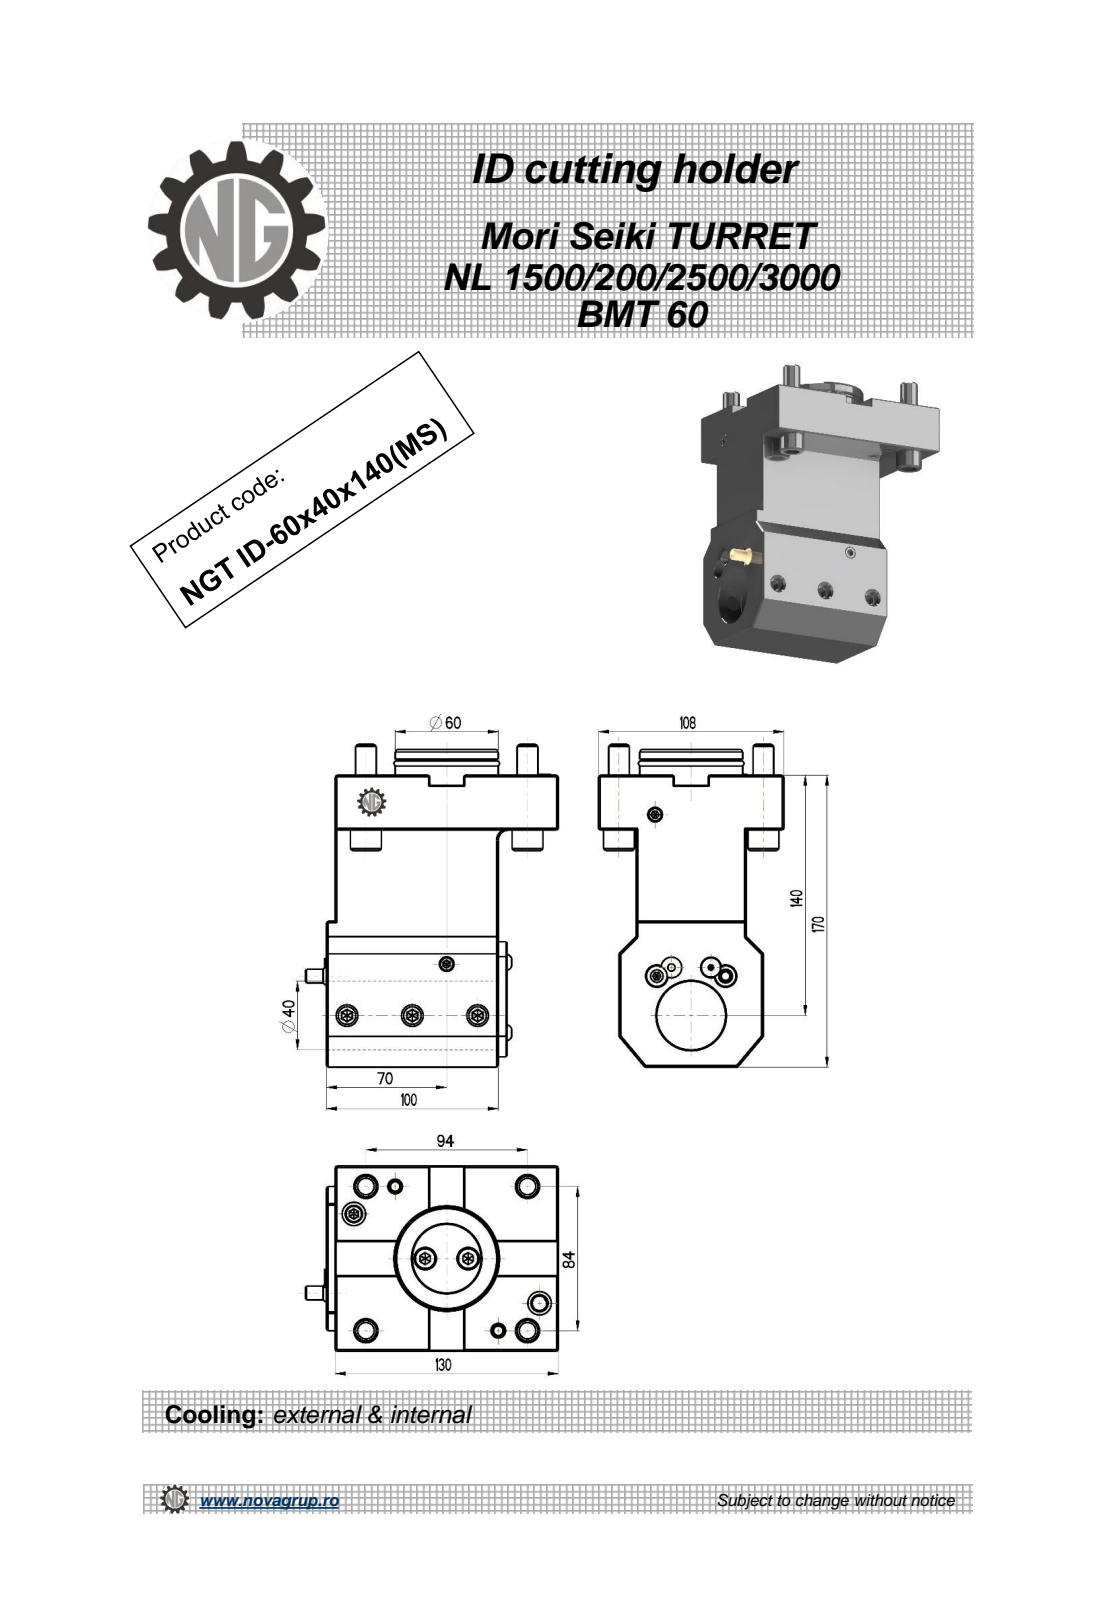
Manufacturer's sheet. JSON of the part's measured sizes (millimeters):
{"part_name": "NGT_ID_60_40_140_MS", "step_written_by": "PRO/ENGINEER BY PARAMETRIC TECHNOLOGY CORPORATION, 2010280 (CONFIG_CONTROL_DESIGN)", "units": "millimeters", "bodies": {"solids": 2, "faces": 606, "planar": 307, "cylindrical": 151, "other": 148}, "overall_size": [188, 147.09, 108], "volume_mm3": 1353000, "surface_area_mm2": 122735, "round_holes": [[10.2, 3], [13.6, 2], [40, 2], [5, 1], [8.5, 1]], "round_bosses_or_shafts": [[18, 4], [12, 4], [13, 2], [59.9, 1], [55.4, 1], [11.2, 1], [8, 1]], "partial_cylinders_radius": [[0.61, 36], [0.36, 20], [0.26, 12], [0.22, 6], [0.51, 6], [4, 1], [6, 1]], "face_to_face_distances": [12, 74, 10, 5, 100, 22, 86, 96, 32, 64], "hole_center_spacings": [38, 59.93, 30.48, 76, 119.87]}
